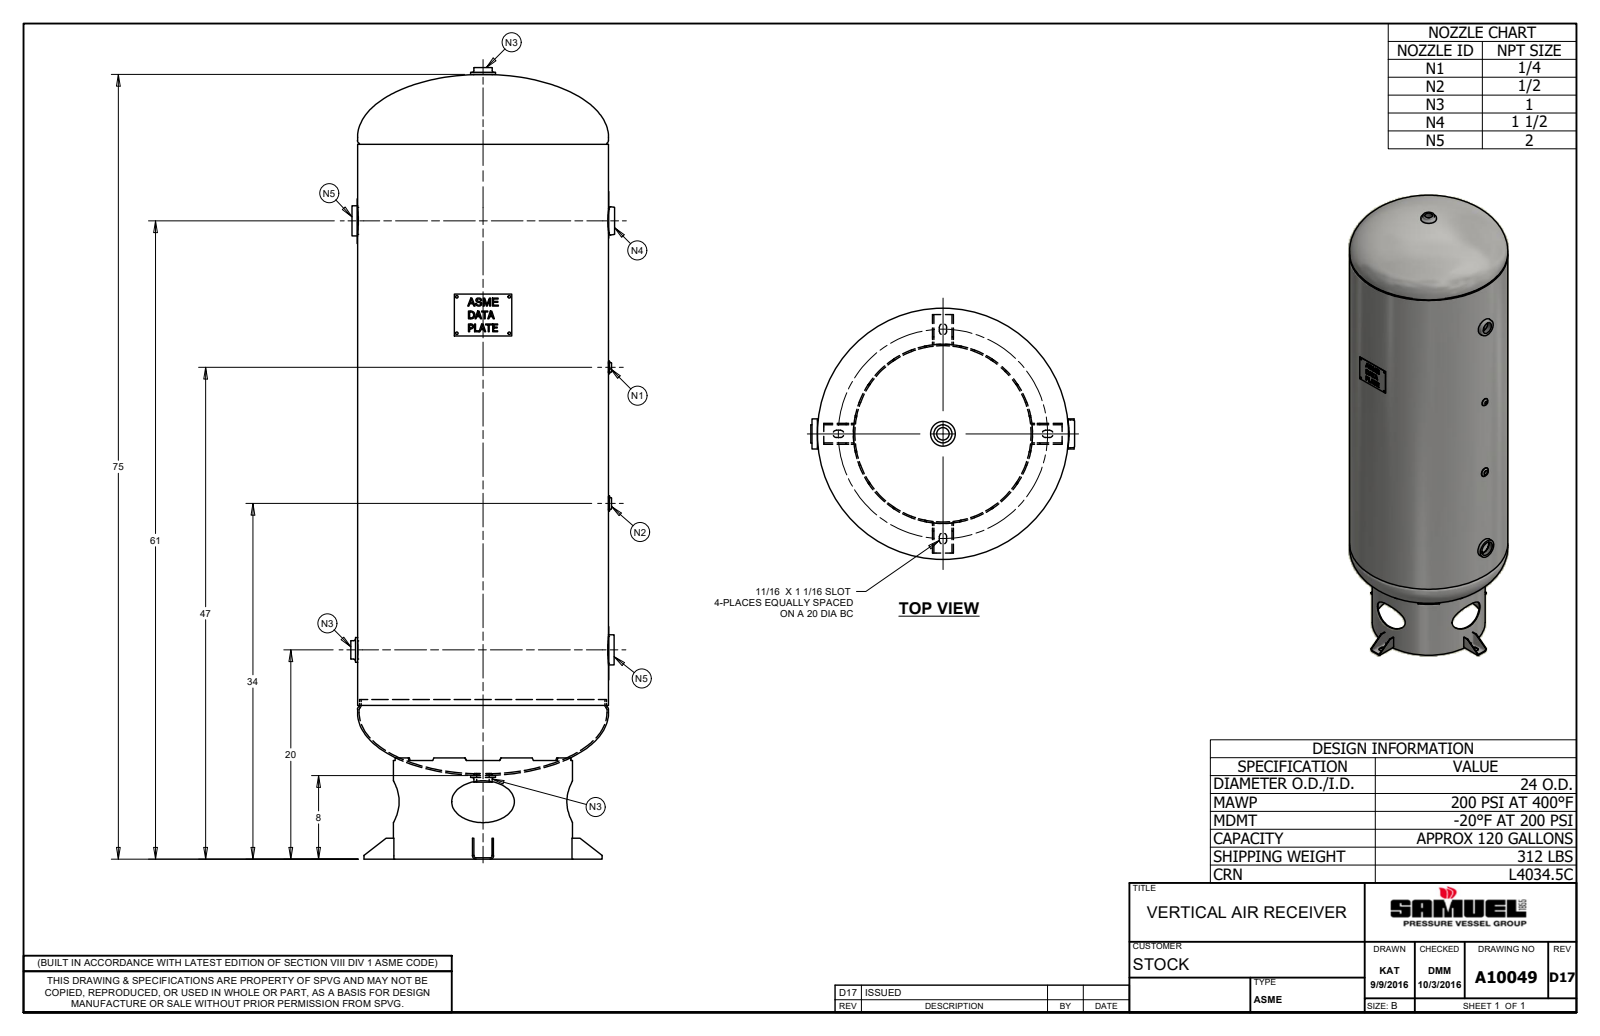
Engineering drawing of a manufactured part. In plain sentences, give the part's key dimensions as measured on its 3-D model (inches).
The part is named "A10049; 37-4089; A10049-3HD; 910-822 (+8 more)". Its 3-D file was written by "Autodesk Inventor 2019 (CONFIG_CONTROL_DESIGN)". It is 17 solids with 433 faces: 256 planar, 77 cylindrical and 100 other. Overall it measures 75.642 by 25.22 by 24.048 inches. Its volume is 1 038 cubic inches and its surface area 12 044 square inches. Round holes: 4 of diameter 0.25, 2 of diameter 1.193, 2 of diameter 2.172, 2 of diameter 2.687, 1 of diameter 0.451, 1 of diameter 0.734, 1 of diameter 1.03, 1 of diameter 1.219, 1 of diameter 1.766, 1 of diameter 1.766, 1 of diameter 1.813, 1 of diameter 2.329. Round bosses or shafts: 2 of diameter 2.875, 2 of diameter 2.563, 2 of diameter 2.375, 2 of diameter 1.75, 2 of diameter 1.703, 1 of diameter 24, 1 of diameter 23.625, 1 of diameter 17.125. Partial cylindrical surfaces (rounded edges, fillets, slot ends): 8 of radius 0.344, 4 of radius 0.187, 4 of radius 0.322, 4 of radius 7.37, 1 of radius 7.5. The main face-to-face distances are 0.135, 1.865, 0.563, 53.063, 0.048, 14.687, 68.313, 53.625, 2, 14.553. The hole center spacings are 3.5, 5, 6.103, 14, 27, 13, 41.
